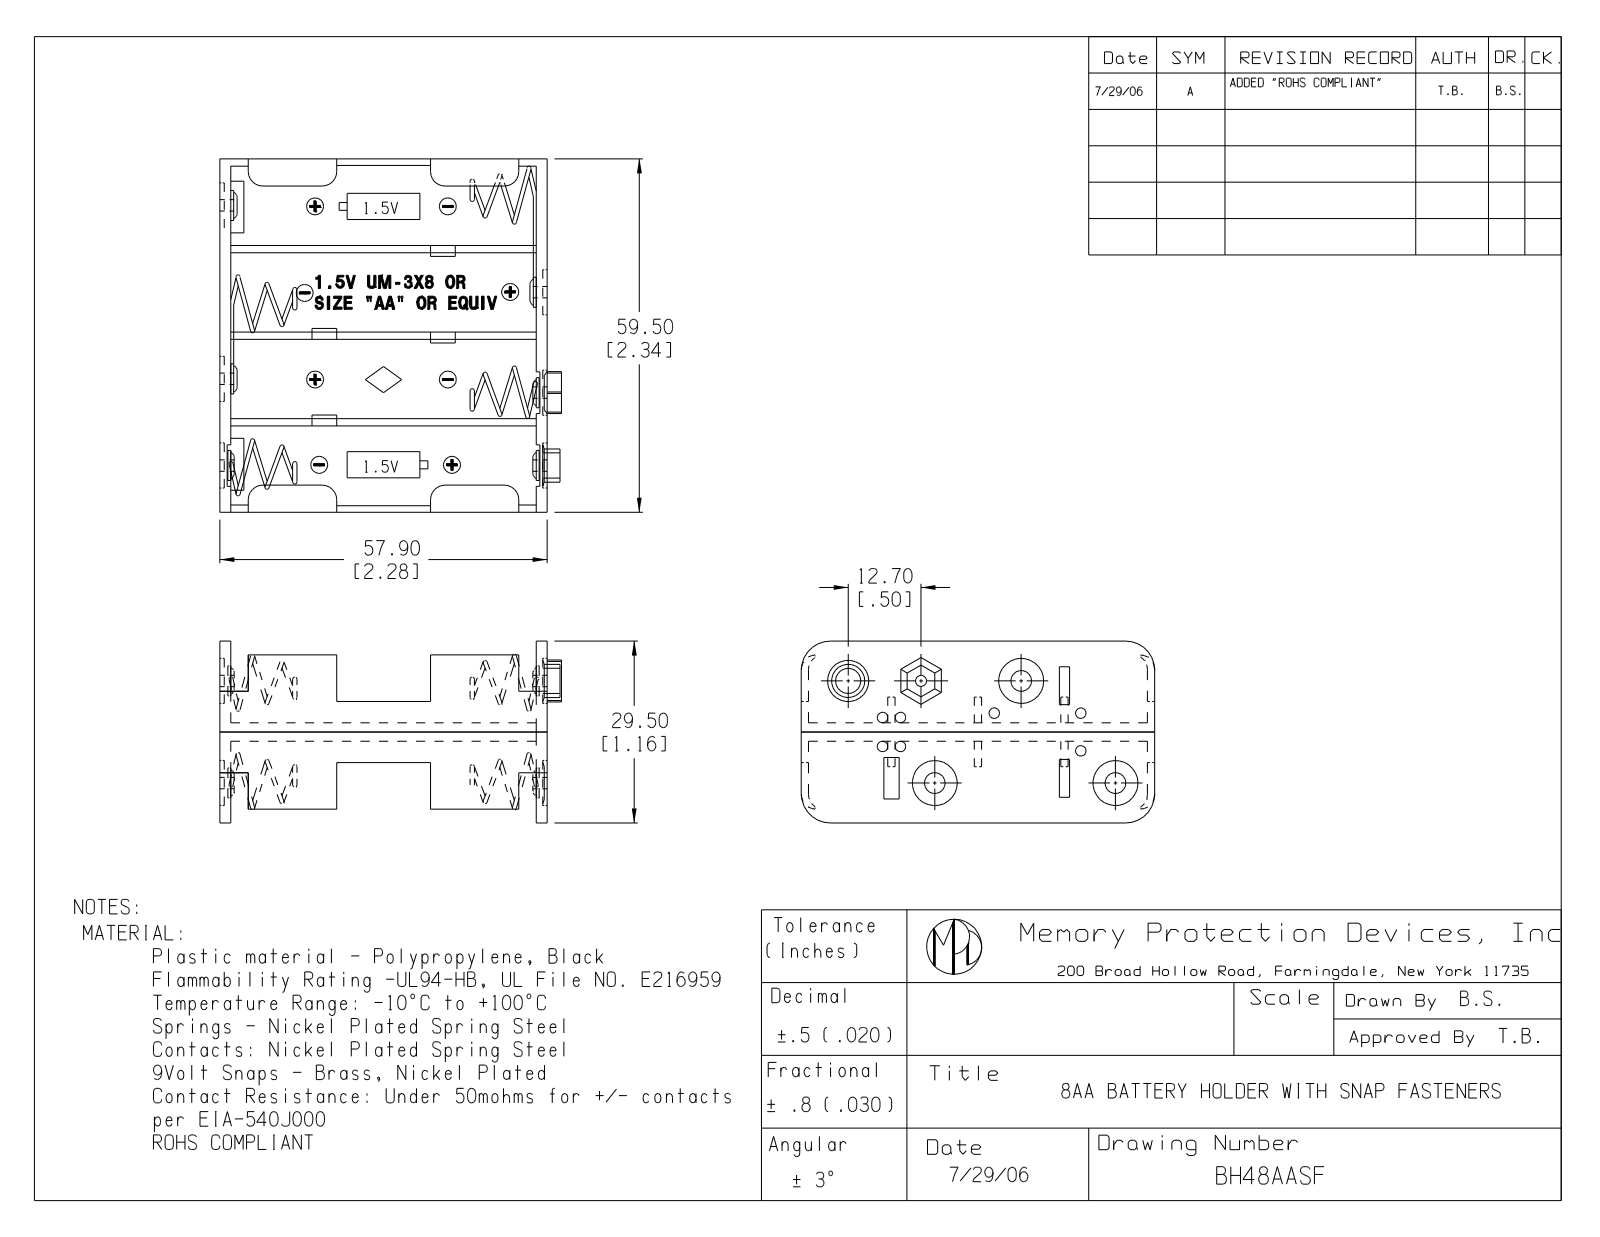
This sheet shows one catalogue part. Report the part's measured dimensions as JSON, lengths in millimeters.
{"part_name": "BH48AASF", "step_written_by": "SolidWorks 2021 (AUTOMOTIVE_DESIGN)", "units": "millimeters", "bodies": {"solids": 13, "faces": 1013, "planar": 549, "cylindrical": 321, "other": 143}, "overall_size": [61.59, 59.5, 29.1], "volume_mm3": 17472, "surface_area_mm2": 24684, "round_holes": [[1.4, 17], [2.2, 9], [8, 9], [3.5, 8], [3.4, 2], [4.95, 1]], "round_bosses_or_shafts": [[3.5, 9], [4.3, 8], [3.4, 7], [0.6, 4], [5.08, 2], [5.72, 1]], "partial_cylinders_radius": [[0.4, 12], [0.89, 6], [2.8, 4], [4, 4]], "face_to_face_distances": [1.2, 2.6, 56.7, 1.3, 58.3, 57.9, 29.1, 55.5, 30.4, 27.9], "hole_center_spacings": [14.69, 15.43, 16.5, 22.09, 26, 29.39, 30.23, 33.7]}
